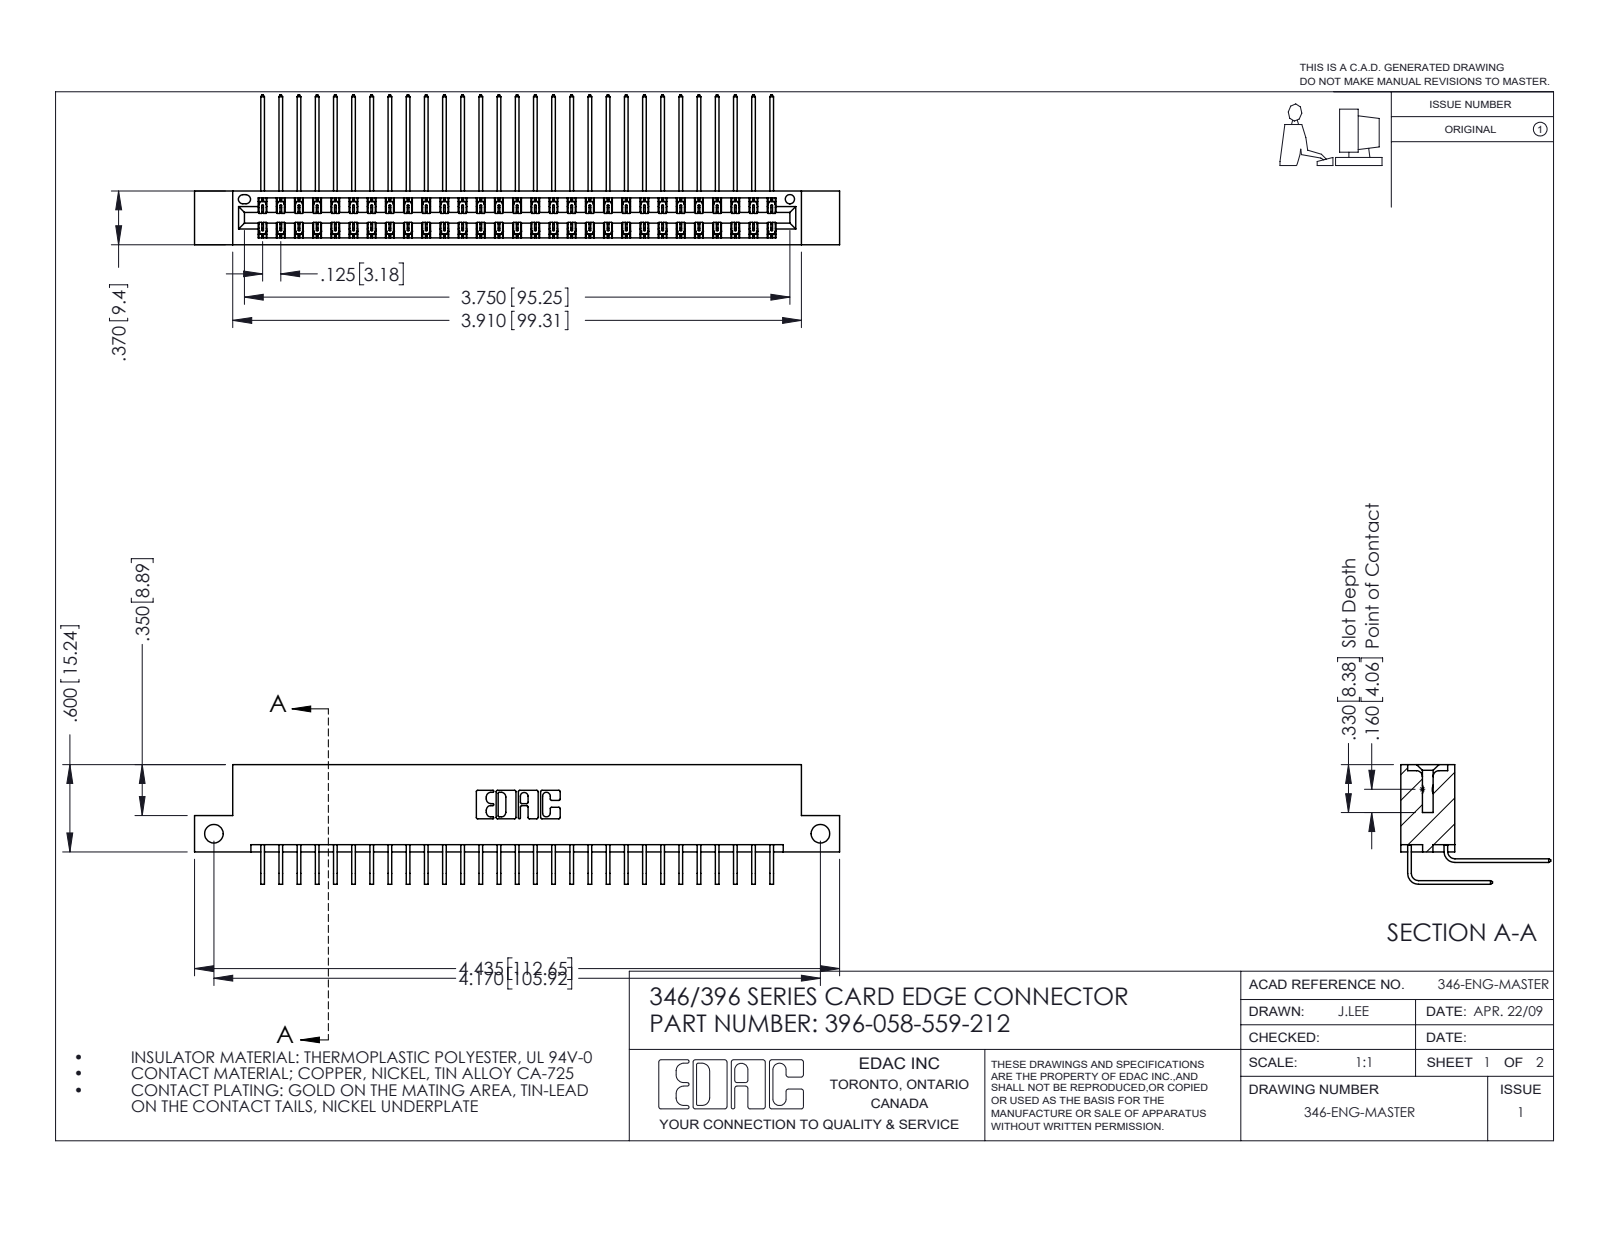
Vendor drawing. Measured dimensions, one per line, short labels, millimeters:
name: 345-292-001_558 559 Tail - 1; 345-292-001_559 Tail - 2; 346 Part_Flush Mounting Lugs - Side Mount; 396-058-559-212
written by: SolidWorks 2016 (CONFIG_CONTROL_DESIGN)
unit: mm
bodies: 59 solids, 3254 faces (2222 planar, 1032 cylindrical, 0 other)
size: 112.6 × 26.2 × 20.9
volume: 11 100 mm³; area: 16 560 mm²
holes: 2× ⌀3.3, 1× ⌀1.6
rounds: 87× R0.2, 22× R0.3, 6× R0.2, 6× R0.8, 3× R0.7, 2× R0.4, 2× R0.6, 2× R0.6
face distances: 1.2, 8.2, 0.6, 6.4, 9.4, 1.8, 7.6, 7, 3.8, 5.6
hole spacings: 105.9
